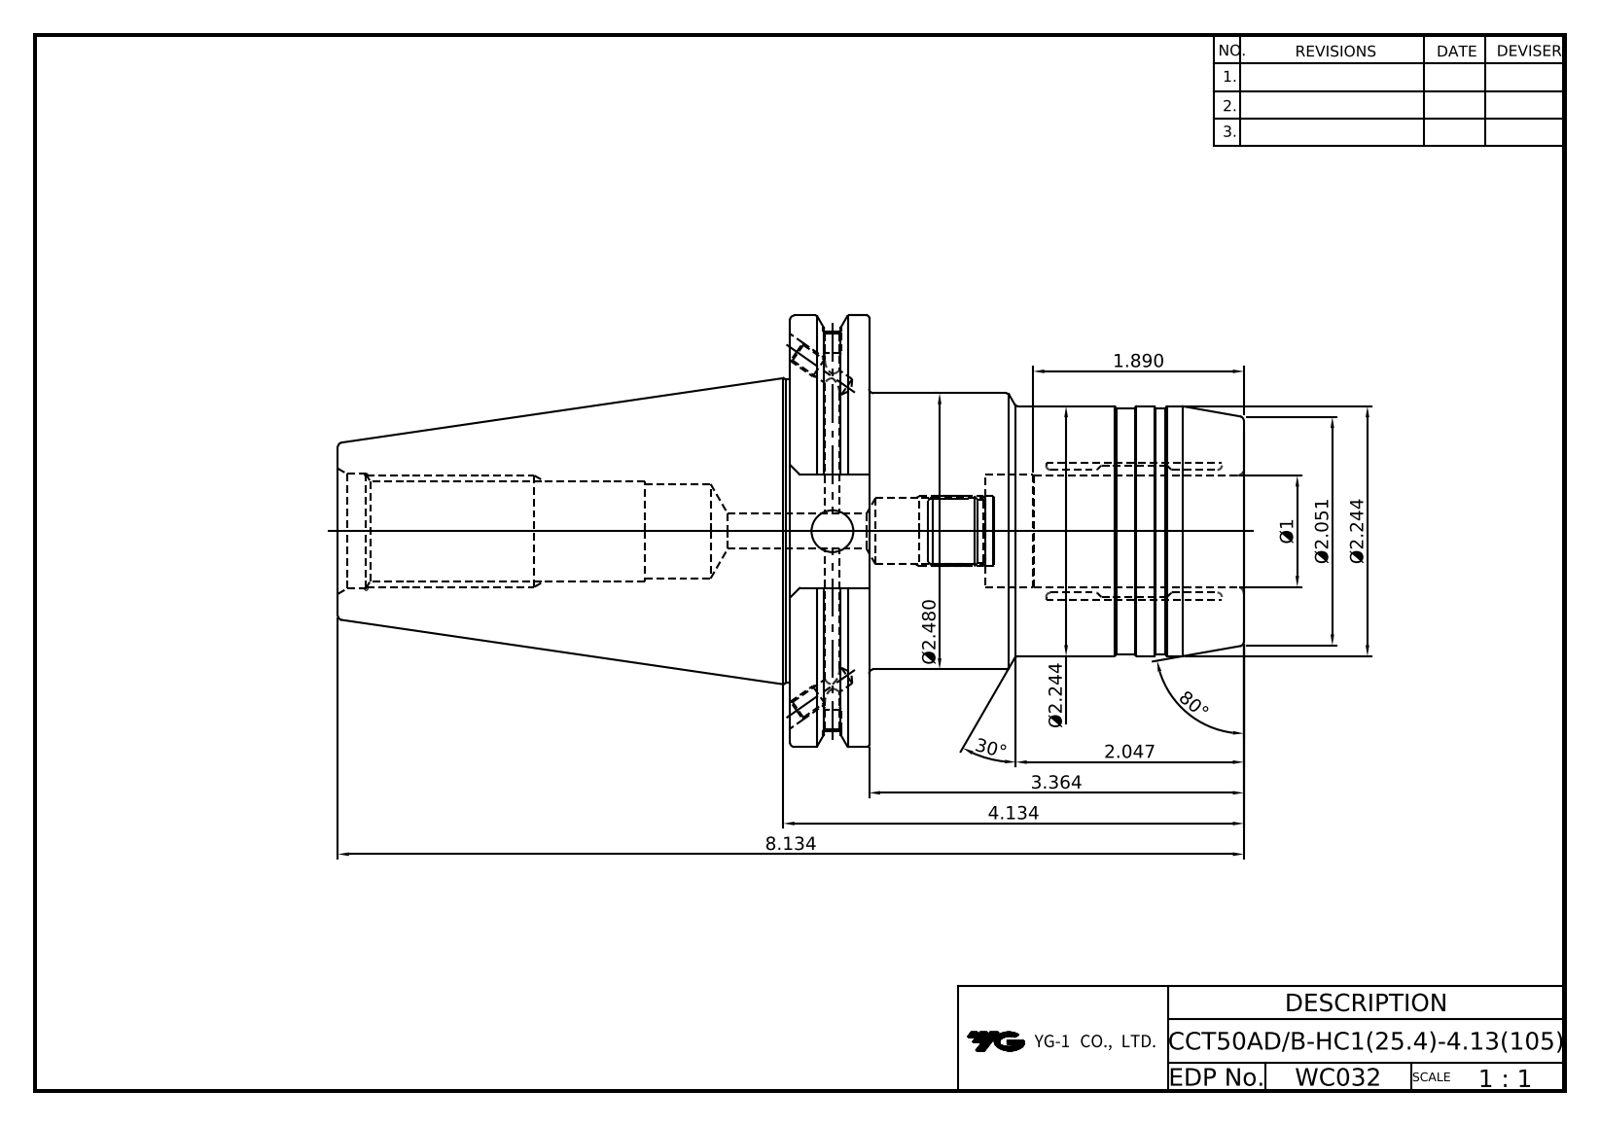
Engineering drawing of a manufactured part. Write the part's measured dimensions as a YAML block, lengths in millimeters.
part_name: "LO-CCT50ADB-HC25.4-105"
step_written_by: "Autodesk Inventor 2020 (AUTOMOTIVE_DESIGN)"
units: millimeters
bodies: {solids: 1, faces: 110, planar: 38, cylindrical: 33, other: 39}
overall_size: [206.6, 98.42, 94.69]
volume: 534307
surface_area: 65349
round_holes:
  - {diameter: 3.24, count: 2}
  - {diameter: 4.13, count: 2}
  - {diameter: 4.2, count: 2}
  - {diameter: 5, count: 2}
  - {diameter: 8, count: 1}
  - {diameter: 9.53, count: 1}
  - {diameter: 14.92, count: 1}
  - {diameter: 21.5, count: 1}
  - {diameter: 21.97, count: 1}
  - {diameter: 25.4, count: 1}
  - {diameter: 25.8, count: 1}
  - {diameter: 26.2, count: 1}
round_bosses_or_shafts:
  - {diameter: 98.42, count: 1}
  - {diameter: 91.29, count: 1}
  - {diameter: 69.25, count: 1}
  - {diameter: 63, count: 1}
  - {diameter: 57, count: 1}
  - {diameter: 56, count: 1}
face_to_face_distances: [17.55, 103.5, 85.95, 103.1, 120.65, 206.6, 73.03, 147.6, 44.5, 26.95]
